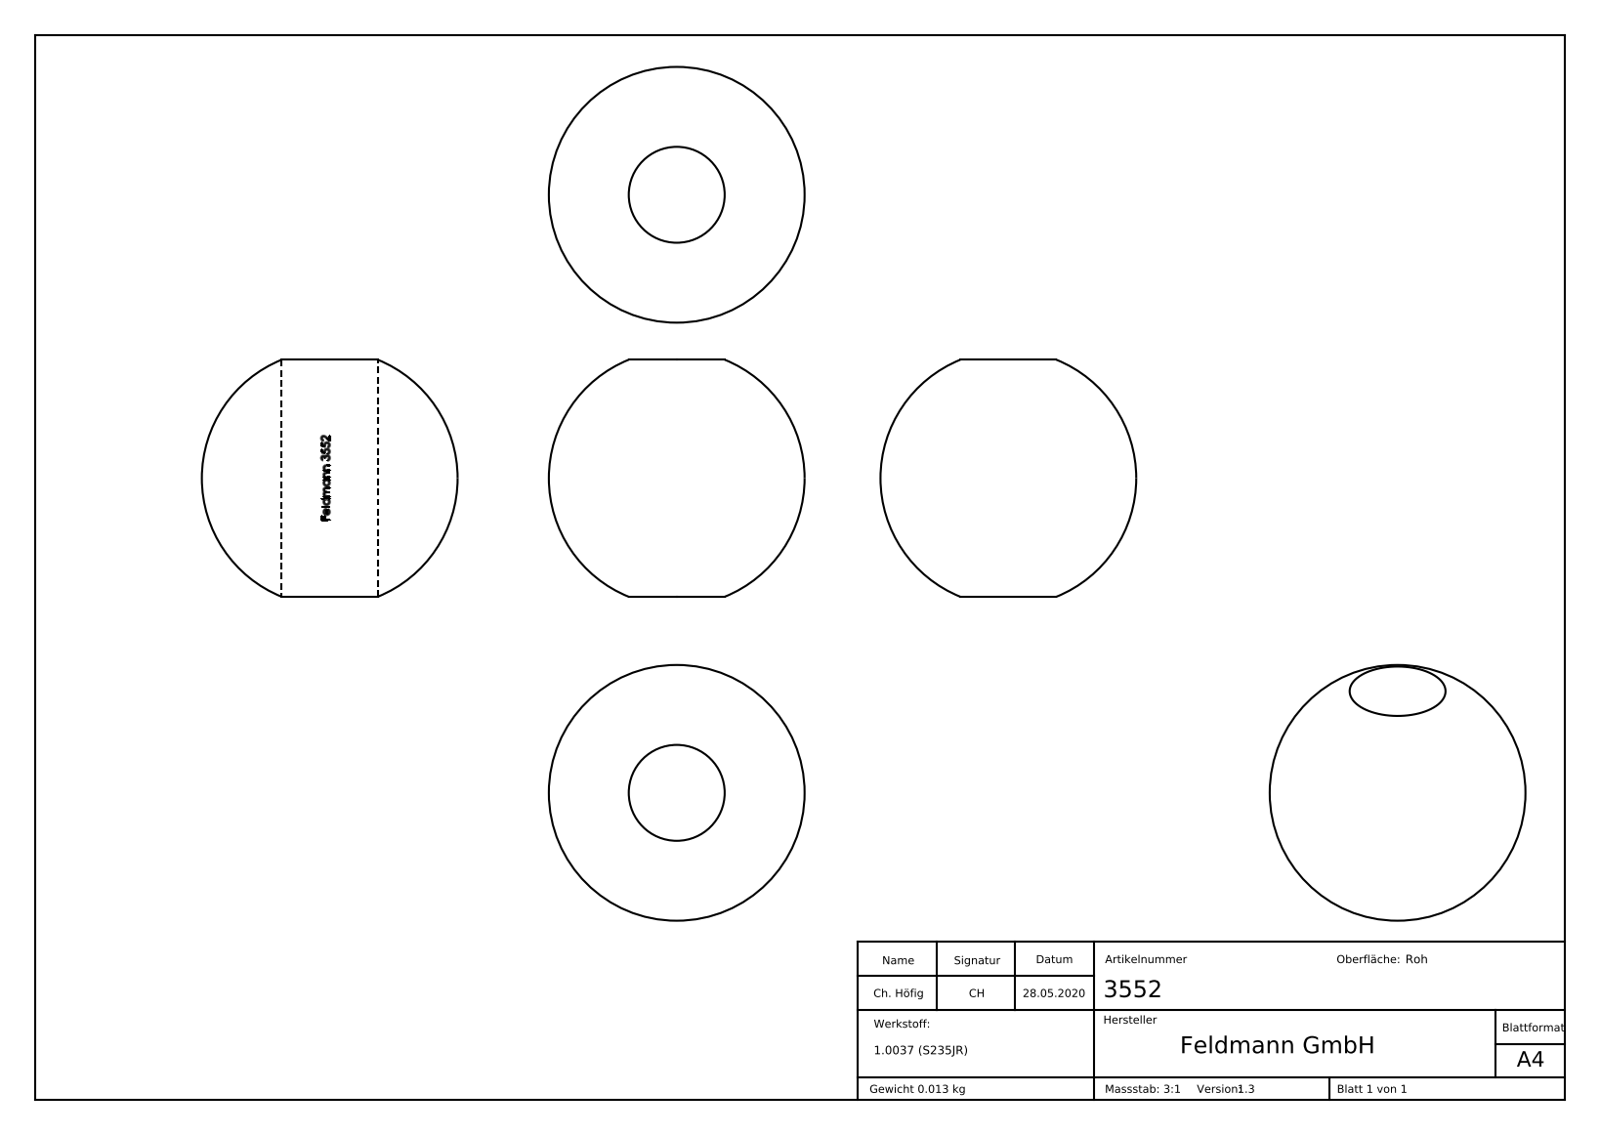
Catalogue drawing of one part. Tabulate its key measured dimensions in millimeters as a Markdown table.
| quantity | value |
| --- | --- |
| part name | 3552 |
| STEP written by | SolidWorks 2015 (CONFIG_CONTROL_DESIGN) |
| units | millimeters |
| bodies | 1 solid, 176 faces (75 planar, 16 cylindrical, 85 other) |
| overall size | 16 × 16 × 14.83 |
| volume | 1 708 mm³ |
| surface area | 1 028 mm² |
| round holes (diameter × count) | 6 × 1 |
| partial cylindrical surfaces (radius × count) | 3.1 × 1 |
| main face-to-face distances | 0.45, 0.55, 0.53, 0.4, 0.5, 0.81, 1.79, 1.84, 1.19, 1.74 |
